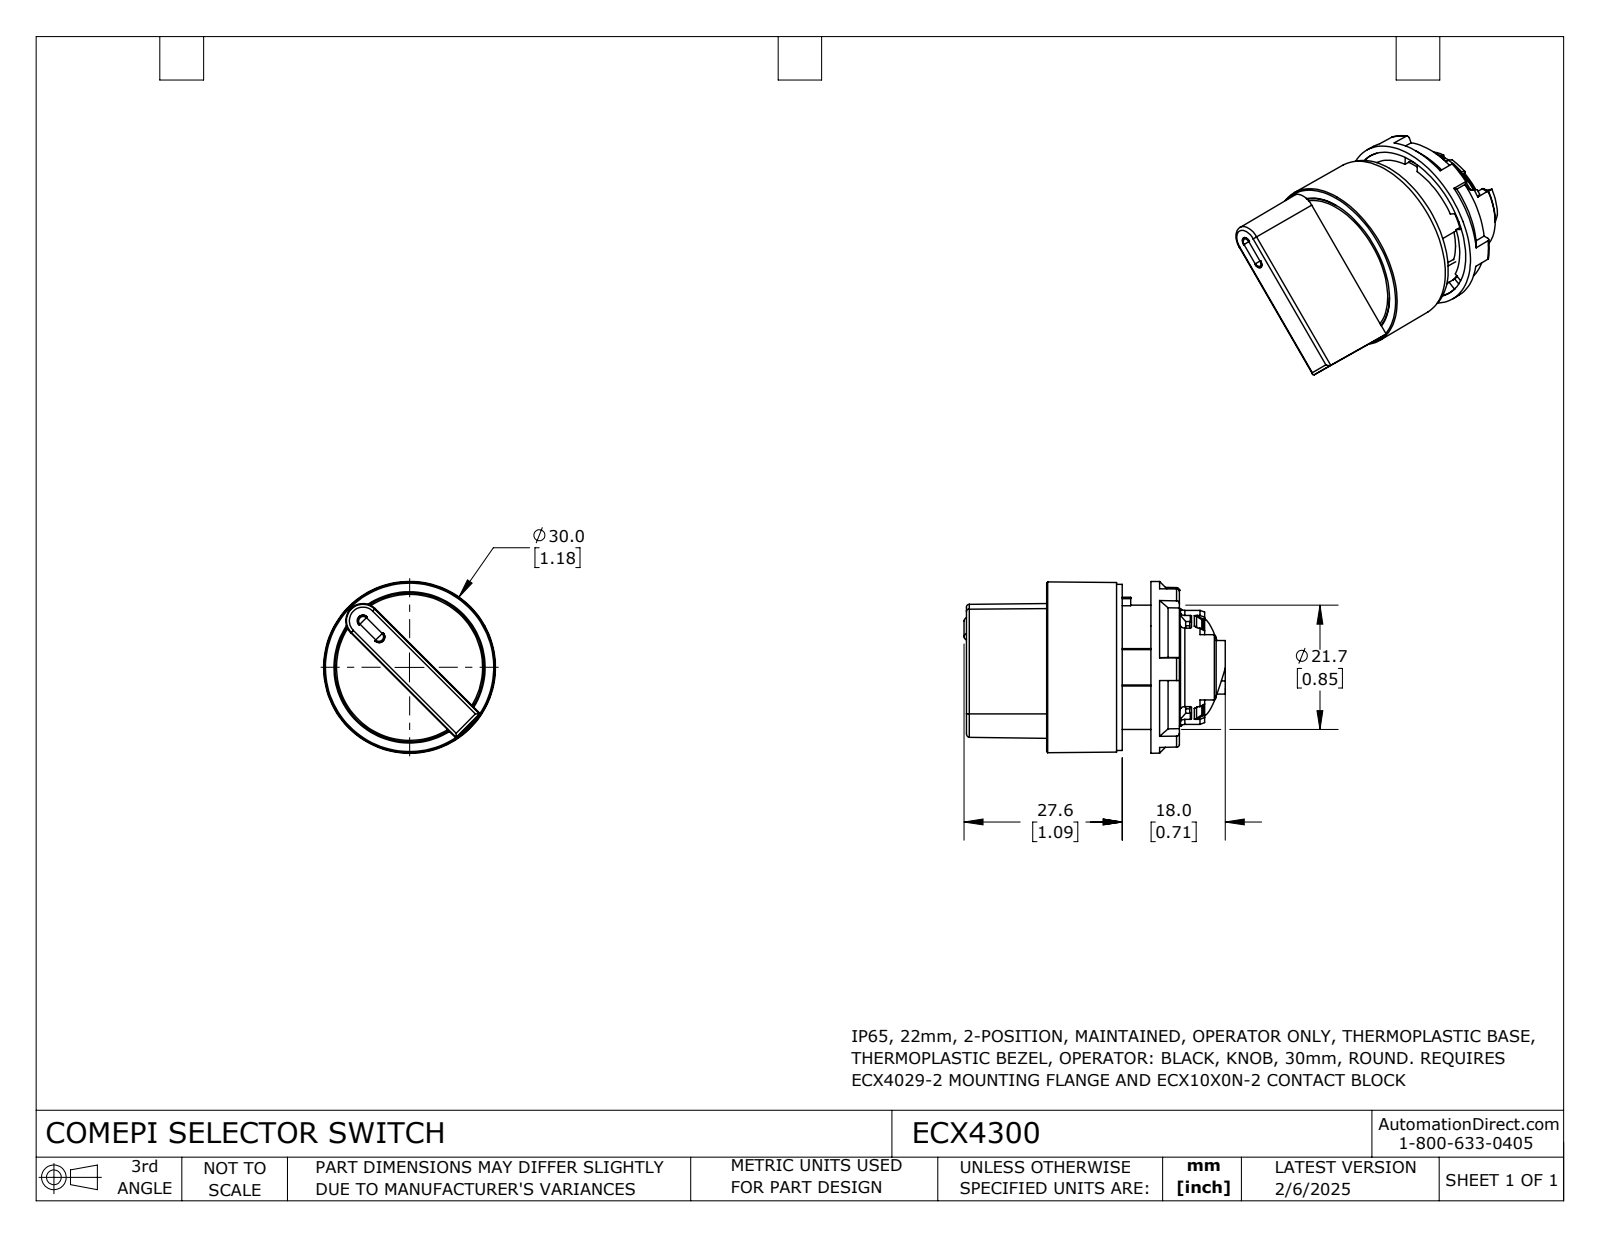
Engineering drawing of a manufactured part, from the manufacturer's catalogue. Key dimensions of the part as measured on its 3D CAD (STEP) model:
Part name (STEP PRODUCT): ECX4300
STEP written by: SolidWorks 2024 (CONFIG_CONTROL_DESIGN)
Units: inches
Bodies: 3 solids, 467 faces (175 planar, 145 cylindrical, 147 other)
Overall size (bounding box): 1.795 × 1.181 × 1.181
Volume: 0.88 in³ · Surface area: 19.73 in²
Round holes (diameter × count): ⌀0.098 ×1, ⌀0.13 ×1, ⌀0.243 ×1, ⌀0.346 ×1, ⌀0.5 ×1, ⌀0.551 ×1, ⌀0.713 ×1, ⌀0.75 ×1, ⌀0.811 ×1, ⌀0.854 ×1, ⌀0.976 ×1, ⌀1.024 ×1
Round bosses / shafts (diameter × count): ⌀1.142 ×1, ⌀1.004 ×1, ⌀0.965 ×1, ⌀0.85 ×1, ⌀0.807 ×1, ⌀0.787 ×1, ⌀0.689 ×1, ⌀0.681 ×1
Partial cylindrical surfaces — rounded edges, fillets, slot ends (radius × count): R0.008 ×24, R0.02 ×7, R0.039 ×5, R0.01 ×2, R0.012 ×2, R0.293 ×1, R0.348 ×1, R0.366 ×1
Main face-to-face distances: 0.48, 0.039, 0.421, 0.118, 0.24, 0.197, 0.913, 0.52, 0.079, 0.402
